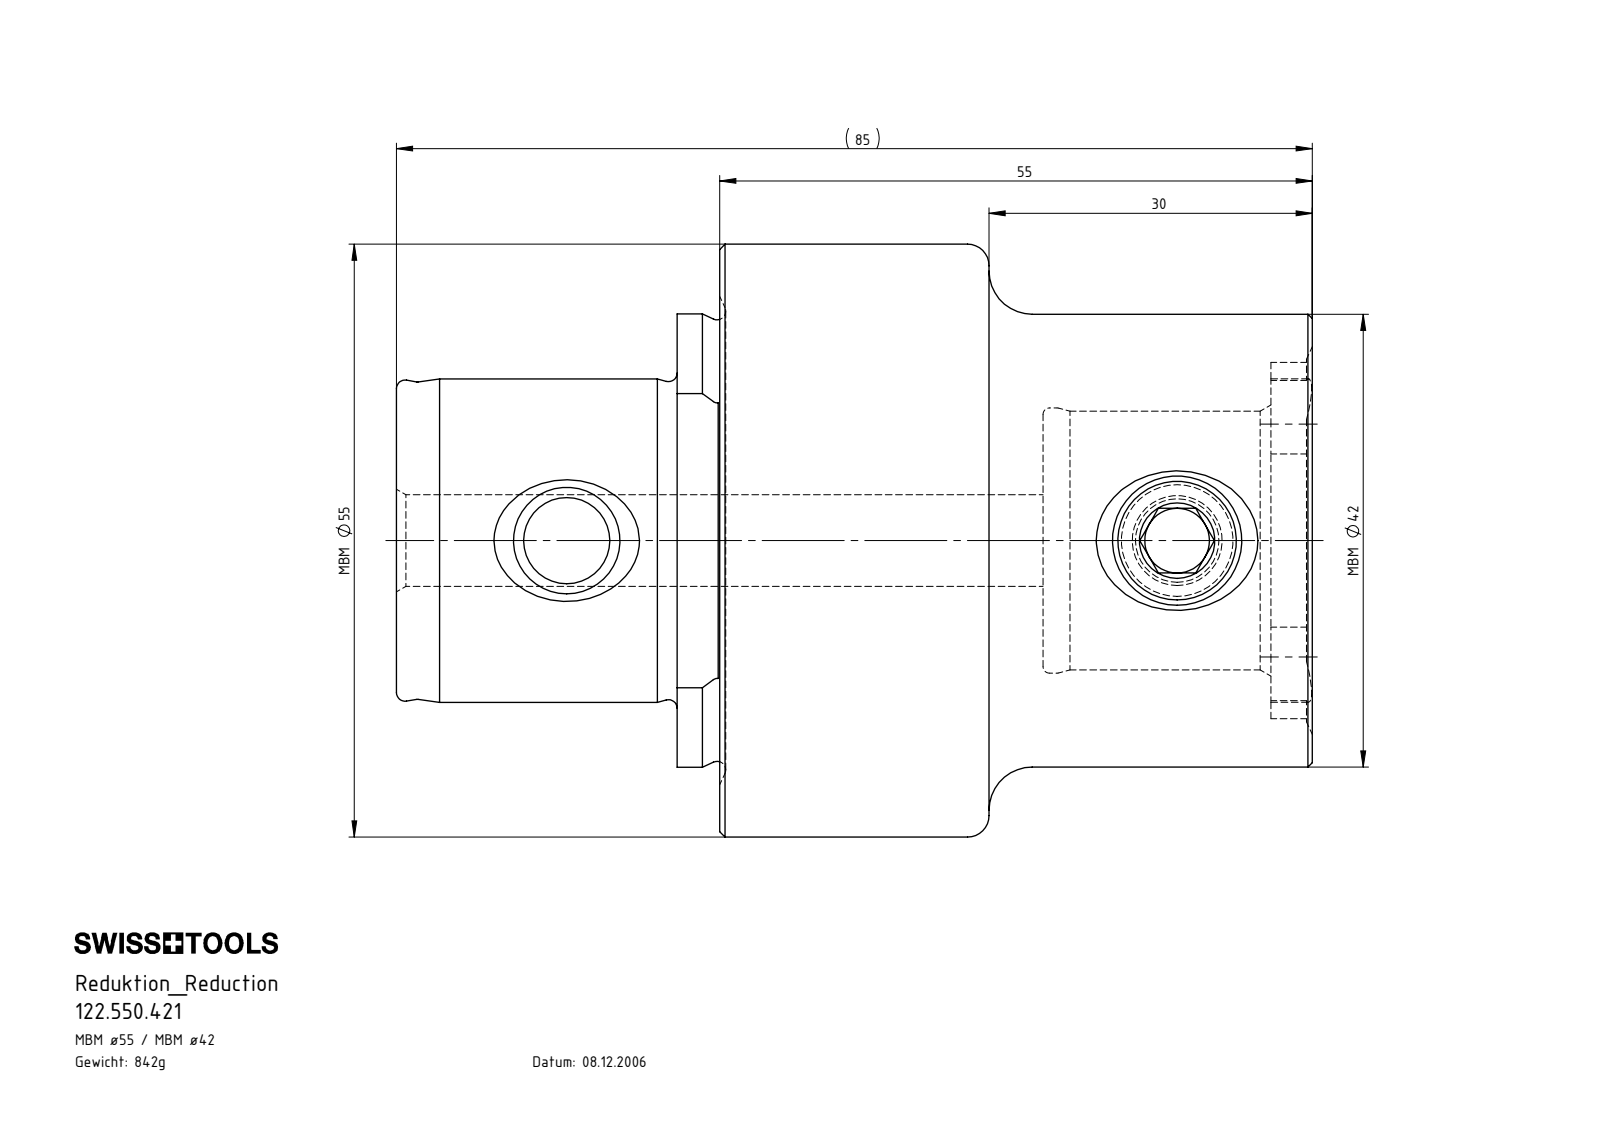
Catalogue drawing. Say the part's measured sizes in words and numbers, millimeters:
The part is named "MB4-ER1.001.013_A; MB5.MB4.K01.055; MB5-MB4.K01.055_C". Its 3-D file was written by "SolidWorks 2017 (AUTOMOTIVE_DESIGN)". It is 2 solids with 82 faces: 33 planar, 20 cylindrical and 29 other. Overall it measures 85 by 55 by 55 millimeters. Its volume is 107 317 cubic millimeters and its surface area 19 987 square millimeters. Round holes: 1 of diameter 6, 1 of diameter 8, 1 of diameter 8.5, 1 of diameter 11, 1 of diameter 24, 1 of diameter 24.6. Round bosses or shafts: 1 of diameter 55, 1 of diameter 42, 1 of diameter 30, 1 of diameter 12. Partial cylindrical surfaces (rounded edges, fillets, slot ends): 4 of radius 4.2, 1 of radius 14.9, 1 of radius 16.52, 1 of radius 21.02. The main face-to-face distances are 30, 26.05, 3.95, 55, 25, 60, 33.95, 81.15, 55.1, 51.15. The hole center spacings are 56.65.
